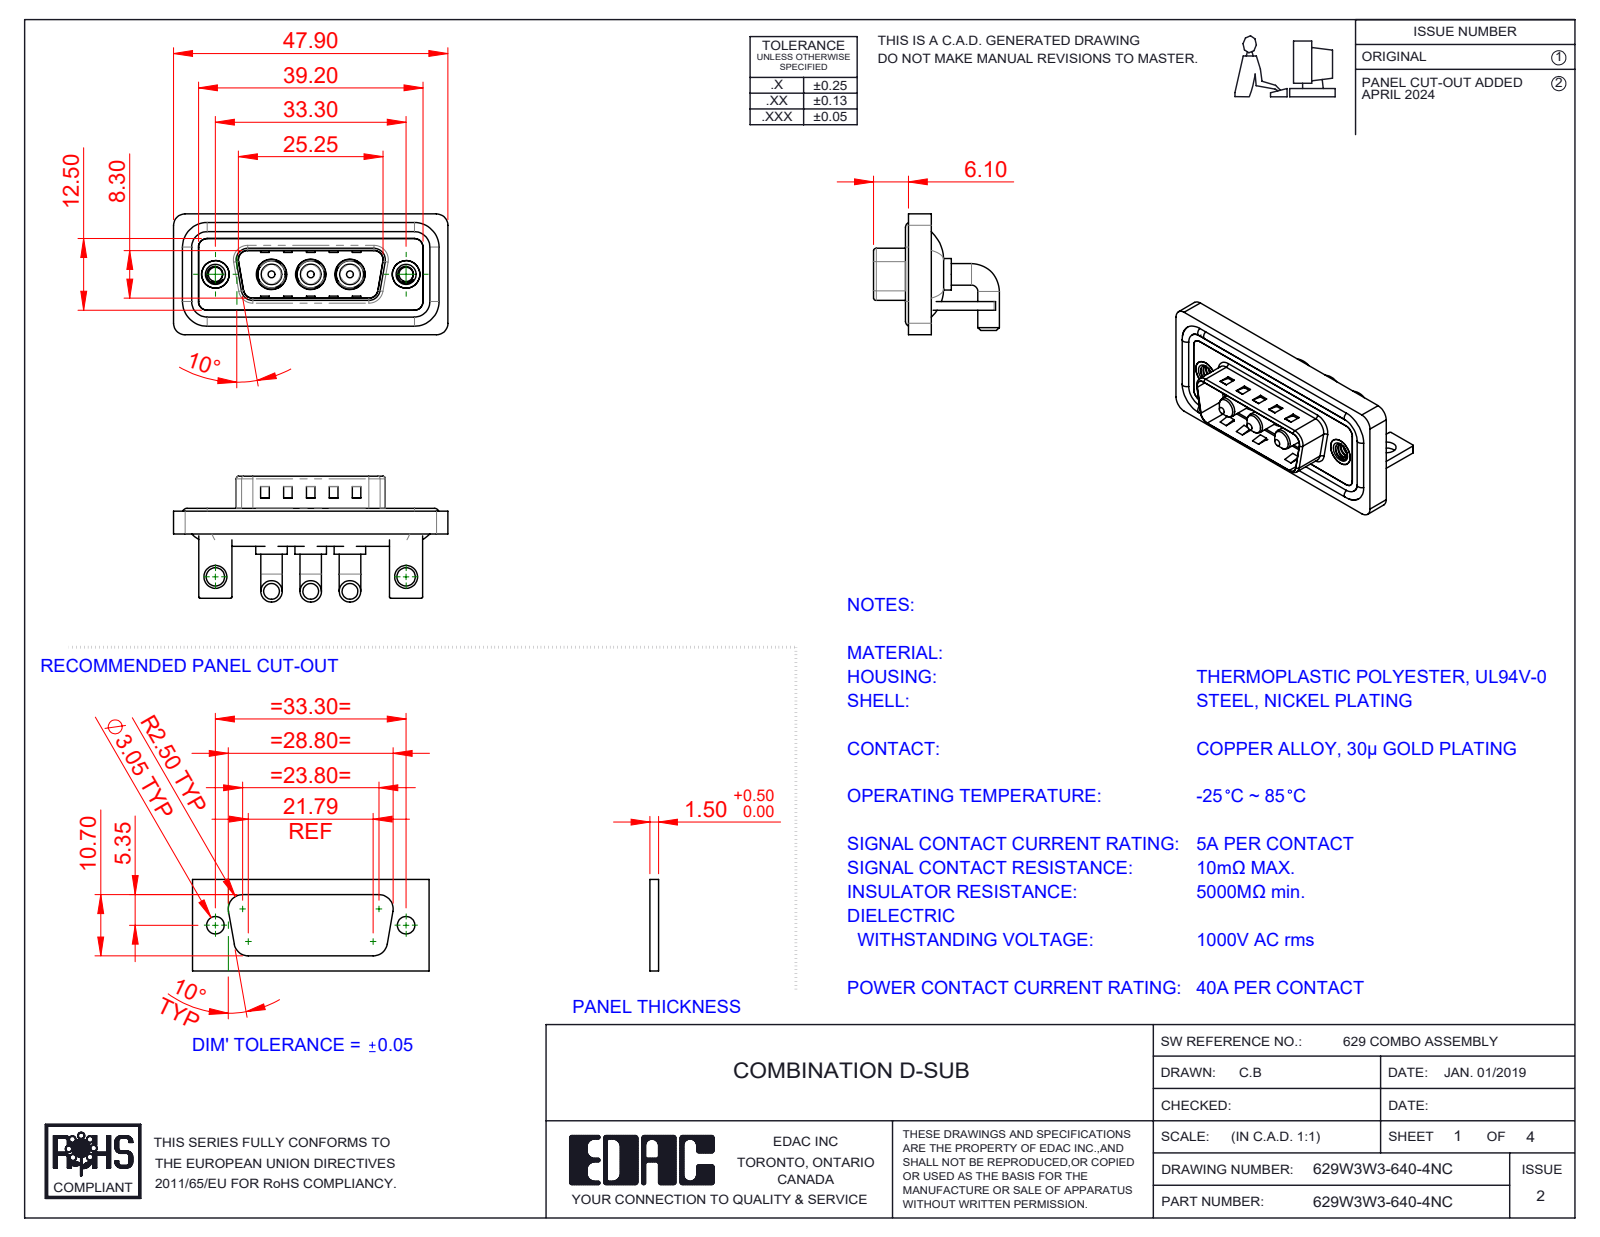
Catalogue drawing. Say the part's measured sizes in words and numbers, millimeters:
The part is named "629Combo Stabilizer Bracket; 629Combo Shell Front_15 Contacts; 629W3W3-640-4NC; 629Combo Waterproof Housing_15 Contacts (+4 more)". Its 3-D file was written by "SolidWorks 2023 (CONFIG_CONTROL_DESIGN)". It is 15 solids with 614 faces: 227 planar, 265 cylindrical and 122 other. Overall it measures 47.9 by 21.98 by 21.1 millimeters. Its volume is 6 269 cubic millimeters and its surface area 9 756 square millimeters. Round holes: 3 of diameter 4.85, 3 of diameter 5.3, 2 of diameter 2.5, 2 of diameter 3.2, 2 of diameter 4, 2 of diameter 4.8, 2 of diameter 5. Round bosses or shafts: 6 of diameter 3.75, 4 of diameter 1.6, 3 of diameter 5.5, 3 of diameter 5.2, 3 of diameter 4.75, 3 of diameter 3.6, 2 of diameter 4.9. Partial cylindrical surfaces (rounded edges, fillets, slot ends): 21 of radius 2, 18 of radius 1.5, 16 of radius 0.25, 9 of radius 0.5, 8 of radius 1.6, 4 of radius 0.6, 4 of radius 0.65, 4 of radius 0.9. The main face-to-face distances are 0.4, 1.5, 0.8, 2.9, 1.1, 2.1, 3.7, 1.6, 1.2, 4.5. The hole center spacings are 6.85, 9.8, 16.65, 23.5, 33.3, 13.7.
